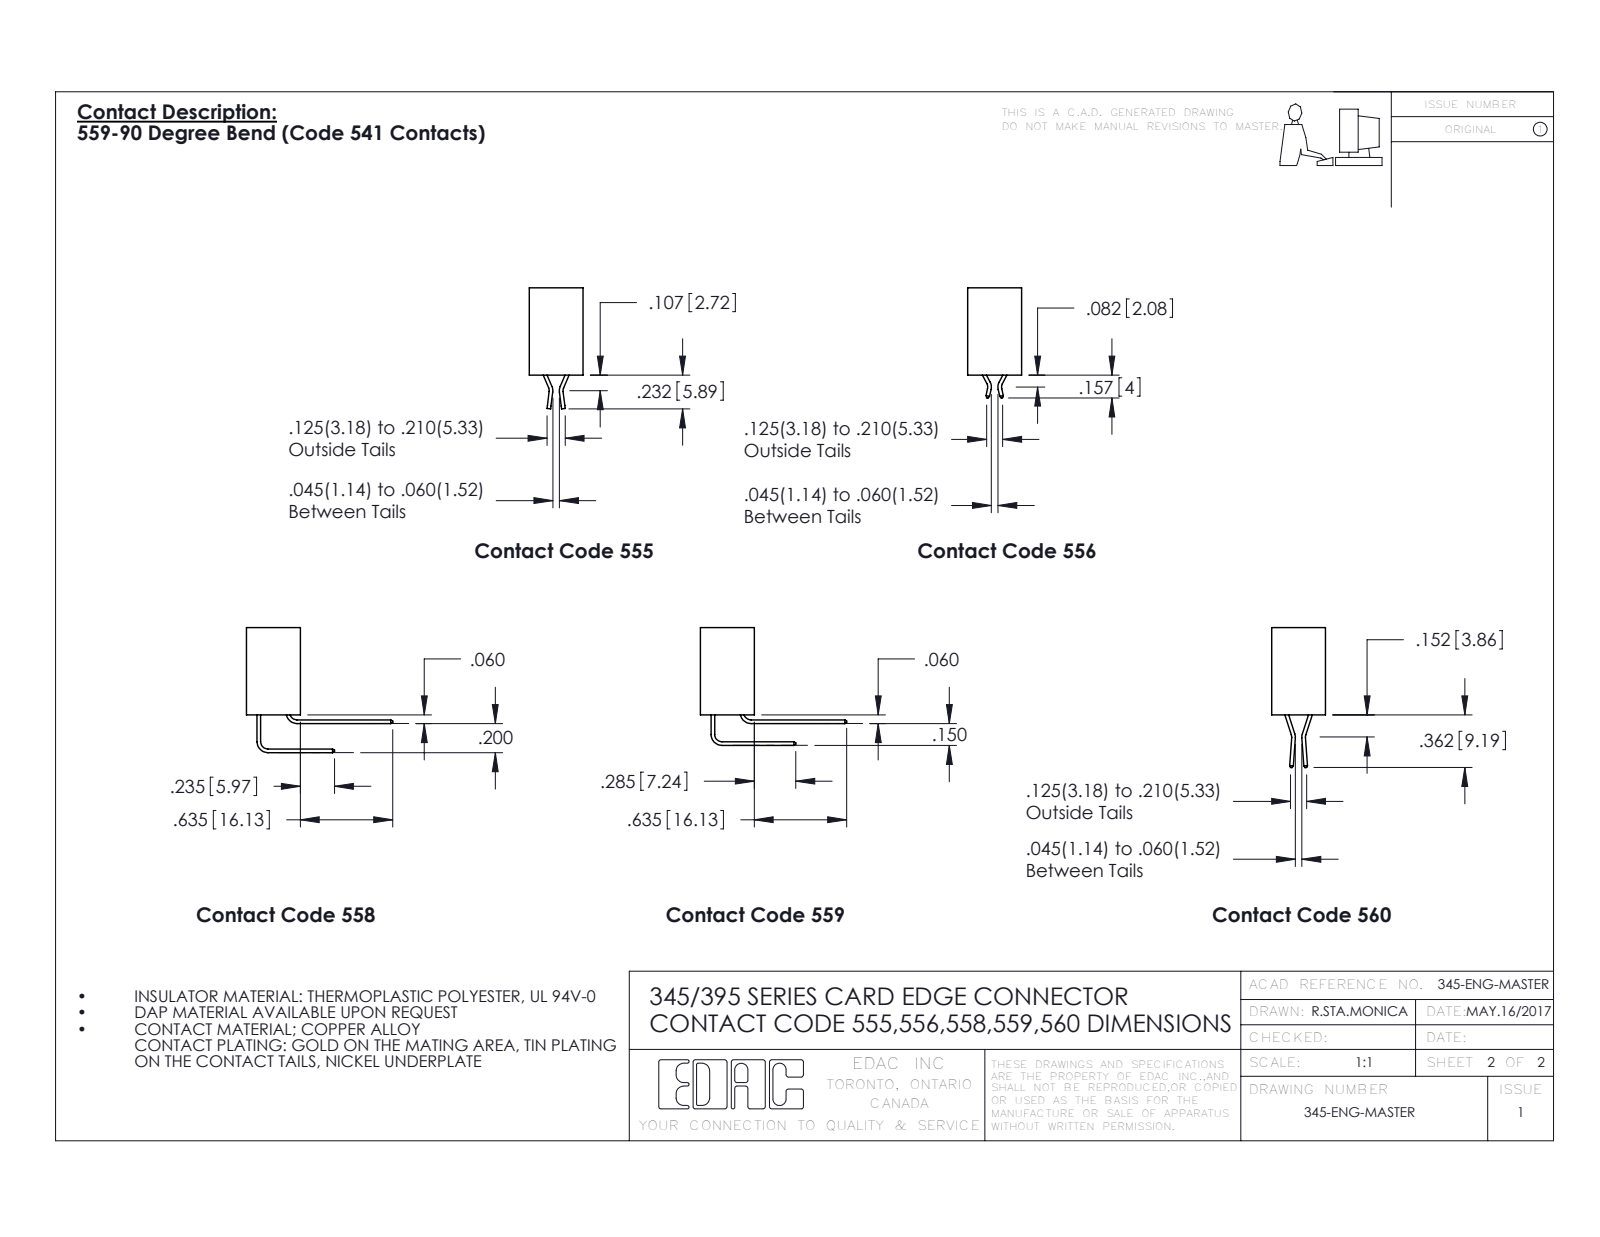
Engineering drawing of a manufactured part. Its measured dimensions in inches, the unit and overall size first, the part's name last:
Units: inches
Overall size (bounding box): 1.36 × 1.005 × 0.859
Round holes (diameter × count): ⌀0.064 ×1
Partial cylindrical surfaces — rounded edges, fillets, slot ends (radius × count): R0.006 ×34, R0.01 ×22, R0.007 ×6, R0.031 ×6, R0.026 ×3, R0.014 ×2, R0.019 ×2, R0.022 ×2
Main face-to-face distances: 0.2, 0.072, 0.298, 0.37, 0.1, 0.098, 0.272, 0.025, 0.6, 0.225
Volume: 0.233 in³ · Surface area: 9.195 in²
Bodies: 23 solids, 1262 faces (846 planar, 416 cylindrical, 0 other)
Part name (STEP PRODUCT): 345 Part_No Mounting Lugs; 395-022-558-201; 345-292-001_558 Tail - 2; 345-292-001_558 559 Tail - 1
STEP written by: SolidWorks 2016 (CONFIG_CONTROL_DESIGN)
